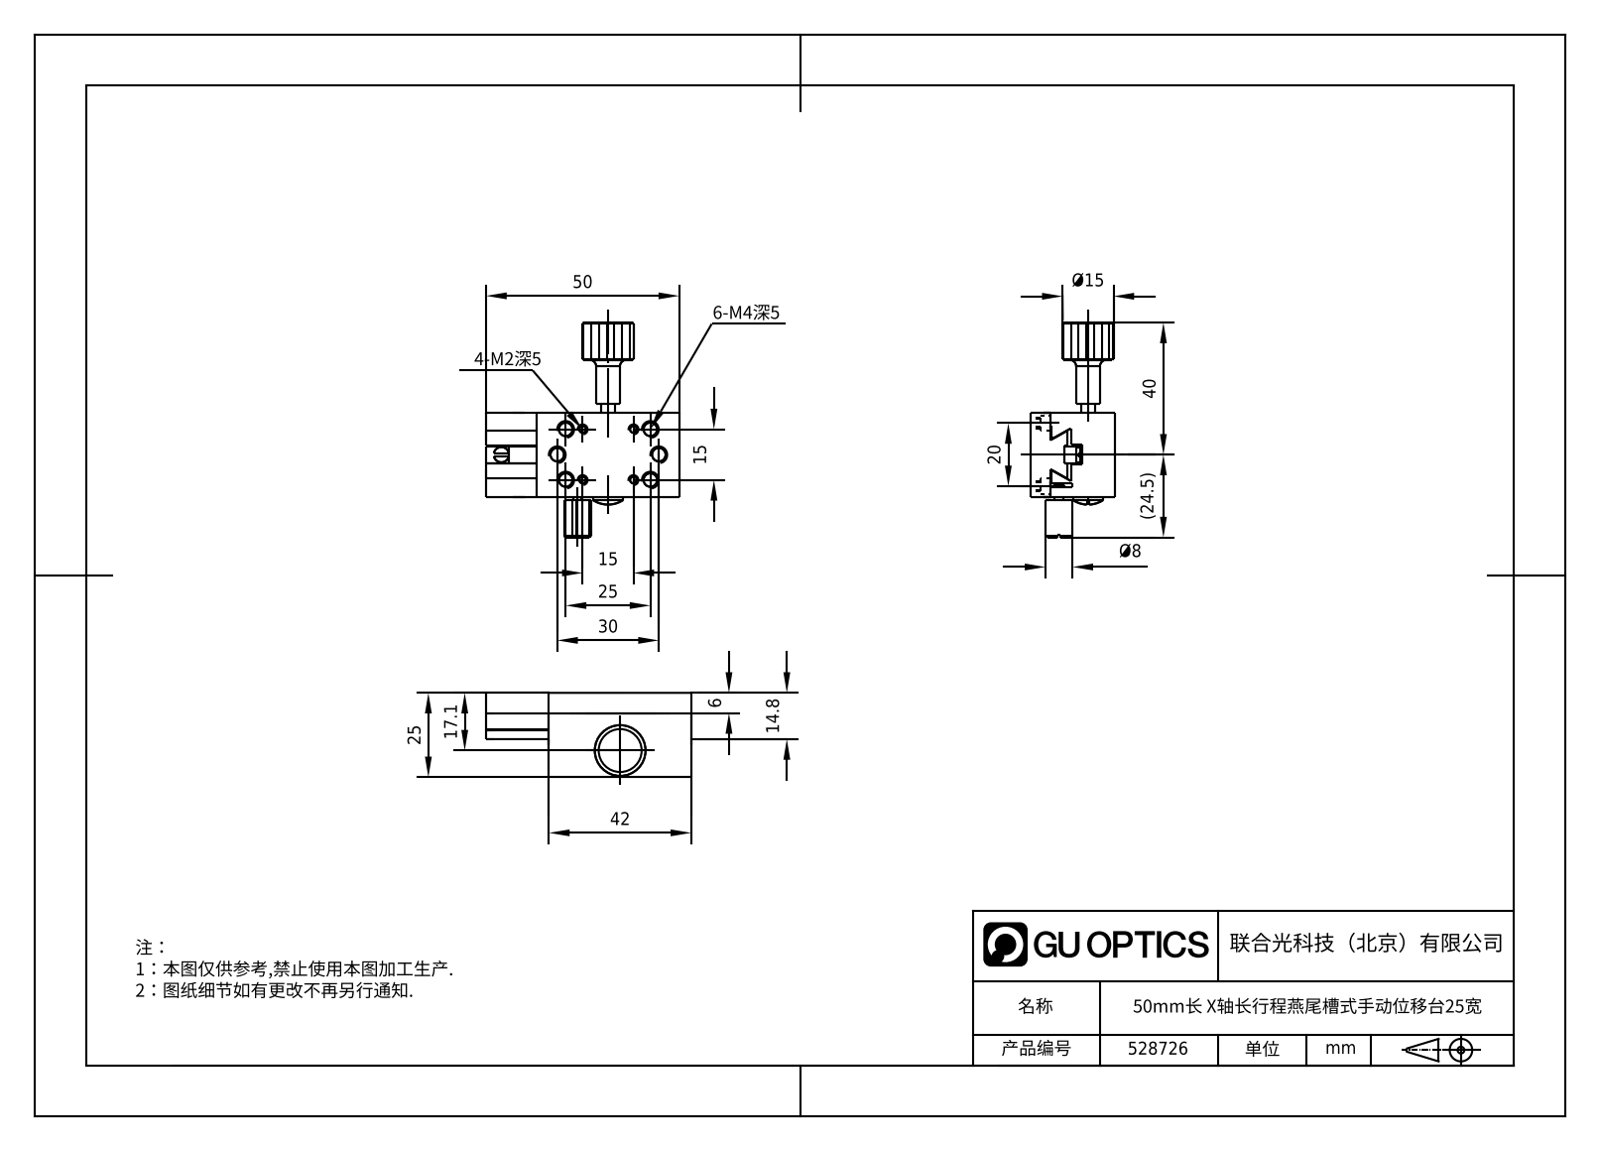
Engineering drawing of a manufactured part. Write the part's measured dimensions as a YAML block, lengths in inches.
part_name: "528726"
step_written_by: "SolidWorks 2020 (CONFIG_CONTROL_DESIGN)"
units: inches
bodies: {solids: 12, faces: 1102, planar: 745, cylindrical: 122, other: 235}
overall_size: [2.489, 1.969, 1.016]
volume: 1.832
surface_area: 25.44
round_holes:
  - {diameter: 0.098, count: 10}
  - {diameter: 0.063, count: 6}
  - {diameter: 0.13, count: 6}
  - {diameter: 0.157, count: 5}
  - {diameter: 0.081, count: 4}
  - {diameter: 0.091, count: 2}
  - {diameter: 0.177, count: 1}
  - {diameter: 0.315, count: 1}
round_bosses_or_shafts:
  - {diameter: 0.354, count: 2}
  - {diameter: 0.15, count: 2}
  - {diameter: 0.098, count: 2}
  - {diameter: 0.079, count: 2}
  - {diameter: 0.276, count: 1}
  - {diameter: 0.27, count: 1}
  - {diameter: 0.256, count: 1}
  - {diameter: 0.118, count: 1}
partial_cylinders:
  - {radius: 0.008, count: 4}
  - {radius: 0.089, count: 2}
  - {radius: 0.177, count: 1}
  - {radius: 0.295, count: 1}
face_to_face_distances: [0.984, 0.63, 0.177, 0.354, 0.157, 0.453, 0.531, 0.185, 1.811, 0.445]
hole_center_spacings: [0.984, 0.315, 0.591, 0.787, 0.098, 0.197, 0.22, 0.311]
